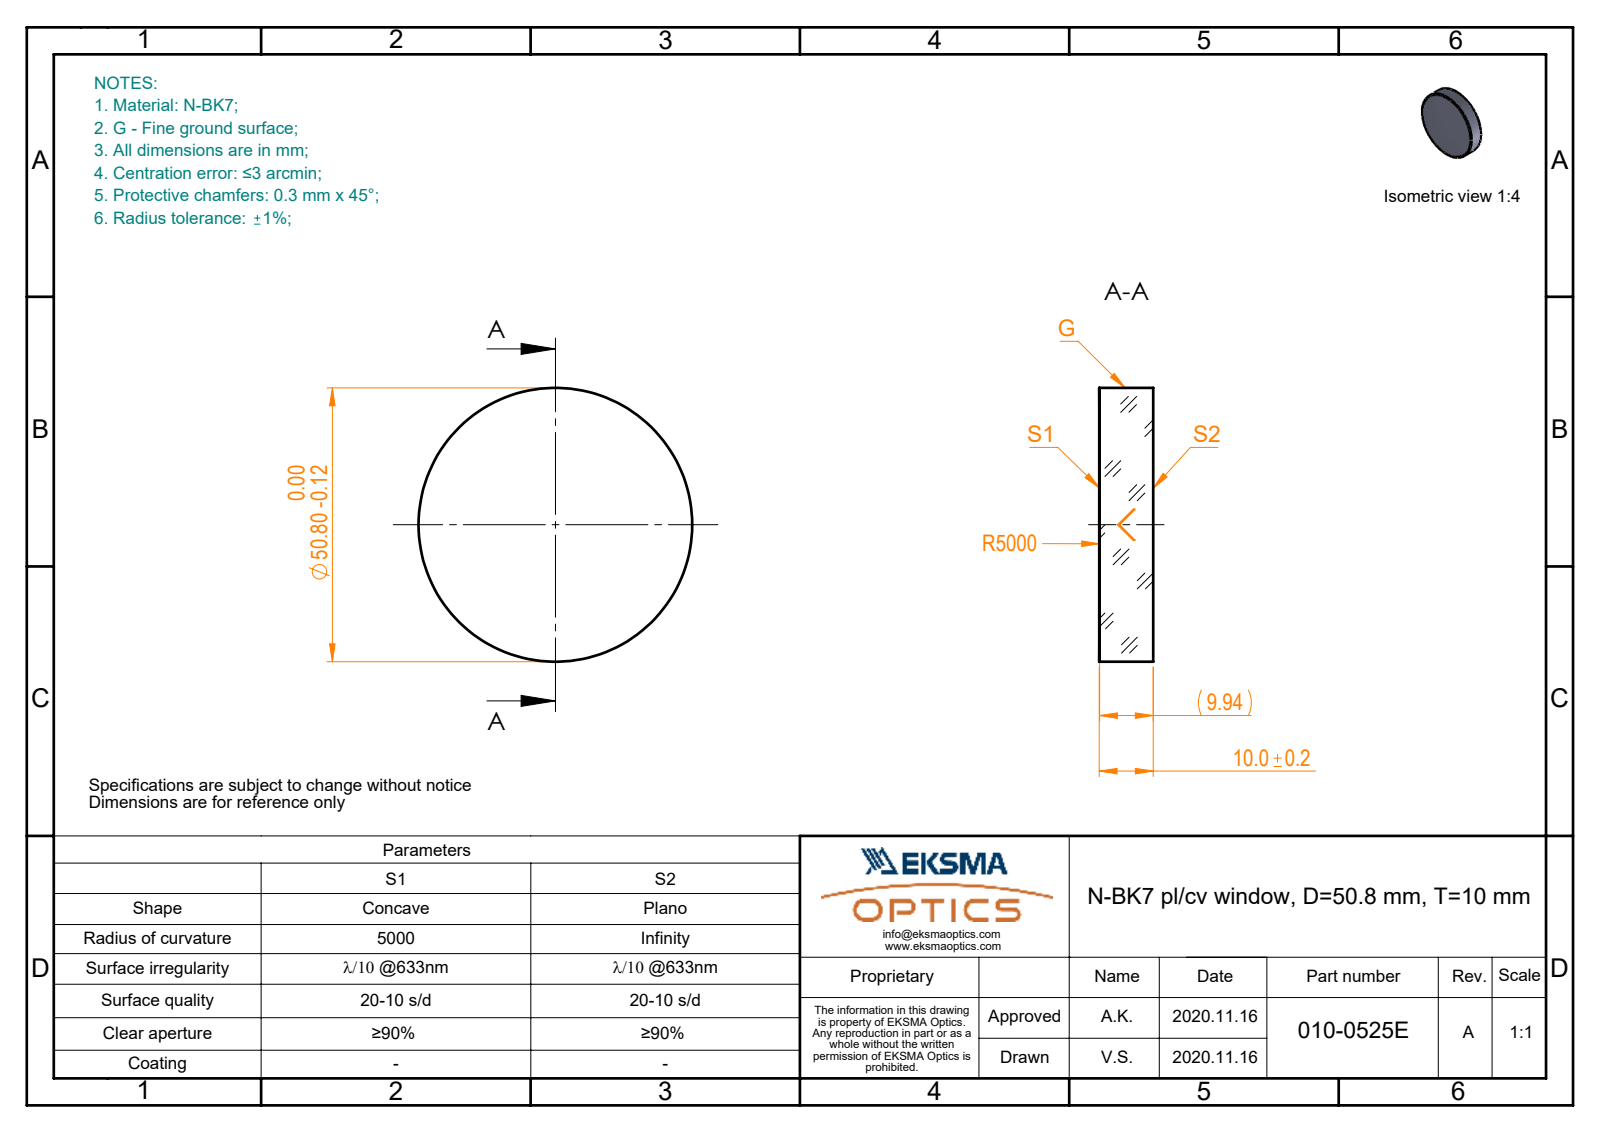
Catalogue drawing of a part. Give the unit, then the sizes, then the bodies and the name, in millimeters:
Units: millimetres
Overall size (bounding box): 50.8 × 50.8 × 10
Round bosses / shafts (diameter × count): ⌀50.8 ×1
Volume: 20 203 mm³ · Surface area: 5 650 mm²
Bodies: 1 solid, 5 faces (1 planar, 2 cylindrical, 2 other)
Part name (STEP PRODUCT): 010-0525E_N-BK7_PCV_window
STEP written by: SolidWorks 2019 (CONFIG_CONTROL_DESIGN)
